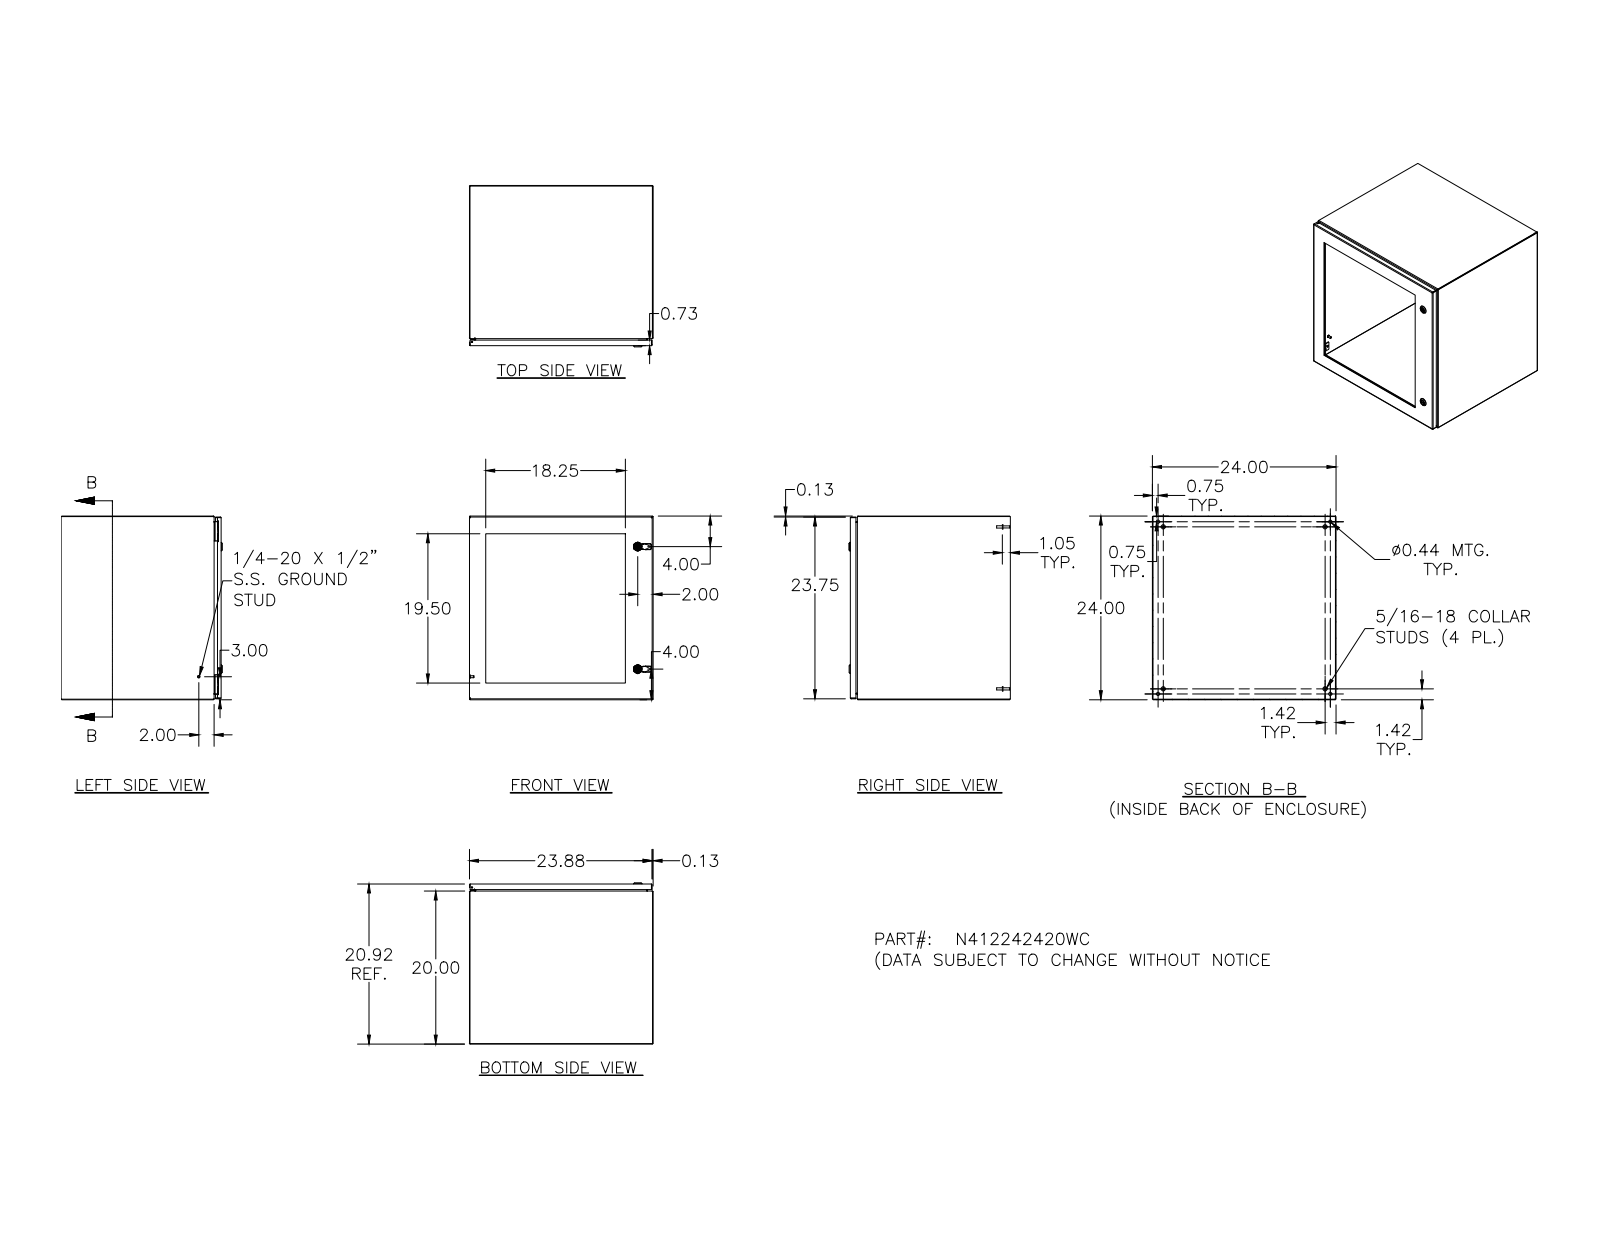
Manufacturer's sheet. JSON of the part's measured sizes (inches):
{"part_name": "N412242420WC", "step_written_by": "SolidWorks 2018 (AUTOMOTIVE_DESIGN)", "units": "inches", "bodies": {"solids": 86, "faces": 2484, "planar": 969, "cylindrical": 746, "other": 769}, "overall_size": [24, 24, 21.075], "volume_in3": 320.5, "surface_area_in2": 6857, "round_holes": [[0.156, 22], [0.281, 20], [0.188, 5], [0.093, 4], [0.152, 4], [0.167, 4], [0.172, 4], [0.438, 4], [0.197, 2], [0.315, 2], [0.394, 2], [0.402, 2]], "round_bosses_or_shafts": [[0.337, 20], [0.19, 20], [0.25, 10], [0.563, 4], [0.36, 4], [0.32, 4], [0.3, 4], [0.256, 4]], "partial_cylinders_radius": [[0.012, 54], [0.031, 33], [0.05, 26], [0.02, 23], [0.105, 22], [0.016, 18], [0.125, 16], [0.032, 8]], "face_to_face_distances": [0.074, 23.926, 23.852, 24, 20.843, 20.769, 0.25, 20.593, 20.519, 20.917], "hole_center_spacings": [4, 8, 21.132, 12, 20, 22.239, 20.75, 6.221]}
